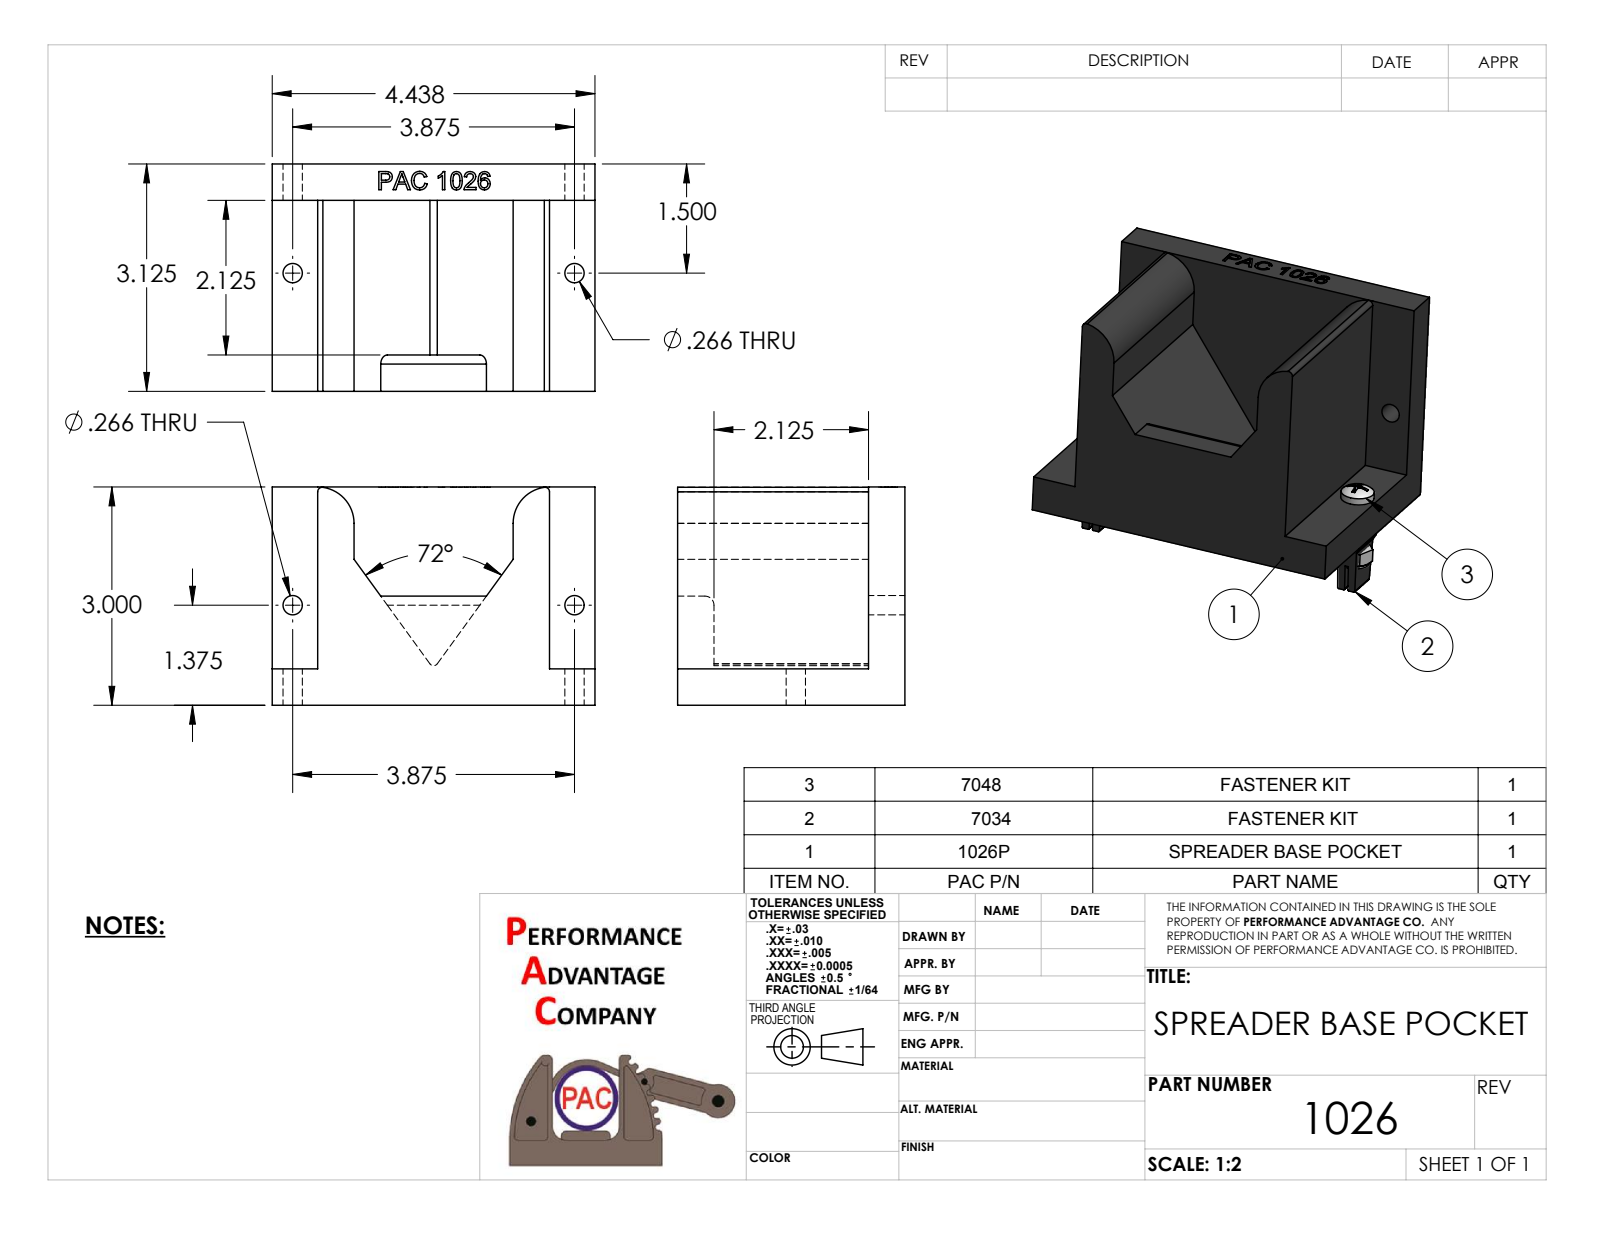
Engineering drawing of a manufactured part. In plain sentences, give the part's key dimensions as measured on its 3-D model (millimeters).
The part is named "1026". Its 3-D file was written by "SolidWorks 2010 (CONFIG_CONTROL_DESIGN)". It is 1 solid with 125 faces: 59 planar, 14 cylindrical and 52 other. Overall it measures 112.7 by 79.4 by 76.2 millimeters. Its volume is 382 300 cubic millimeters and its surface area 53 610 square millimeters. Round holes: 4 of diameter 6.8. Partial cylindrical surfaces (rounded edges, fillets, slot ends): 3 of radius 1.6, 2 of radius 12.7, 1 of radius 3.2. The main face-to-face distances are 12.7, 79.4, 66.7, 80.9, 15.9, 96.9, 112.7, 28.6, 84.2, 68.2. The hole center spacings are 98.4.
